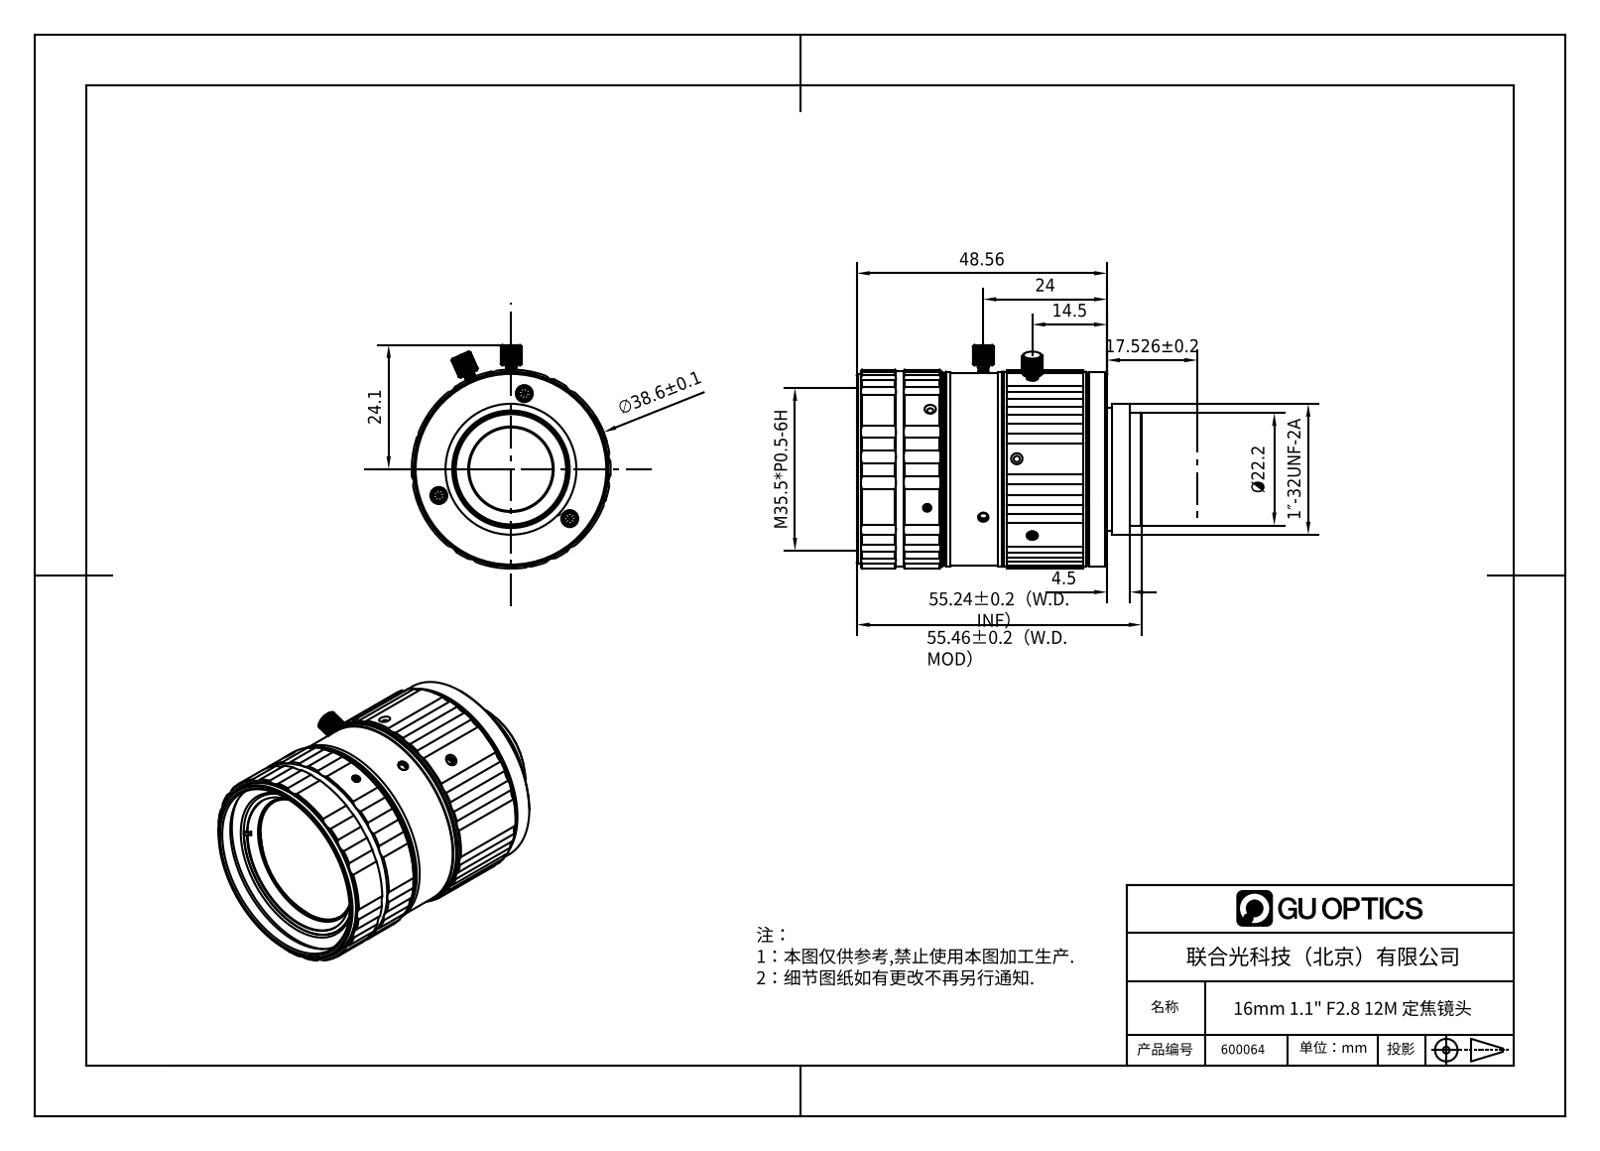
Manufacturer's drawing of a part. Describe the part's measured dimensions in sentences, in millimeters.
The part is named "600064". Its 3-D file was written by "SolidWorks 2020 (CONFIG_CONTROL_DESIGN)". It is 7 solids with 827 faces: 241 planar, 409 cylindrical and 177 other. Overall it measures 55.25 by 43.48 by 38.6 millimeters. Its volume is 54 306 cubic millimeters and its surface area 15 194 square millimeters. Round holes: 6 of diameter 1.6, 3 of diameter 1.8, 3 of diameter 2, 3 of diameter 2, 3 of diameter 2.9, 1 of diameter 16.2, 1 of diameter 16.6, 1 of diameter 20.5, 1 of diameter 22.2, 1 of diameter 25.7, 1 of diameter 28.38, 1 of diameter 30. Round bosses or shafts: 5 of diameter 1.6, 3 of diameter 2.5, 3 of diameter 1.2, 2 of diameter 2, 1 of diameter 38.6, 1 of diameter 37.8, 1 of diameter 37.6, 1 of diameter 37.4. Partial cylindrical surfaces (rounded edges, fillets, slot ends): 6 of radius 1.11, 6 of radius 3.39, 6 of radius 3.43, 2 of radius 1.12, 2 of radius 2, 1 of radius 12.86. The main face-to-face distances are 41.96, 3.3, 45.26, 42.28, 0.32, 2.98, 51.95, 6.69, 48.65, 48.97. The hole center spacings are 25.81, 14.9, 9.5, 14.87, 14.88, 14.91, 14.95.
